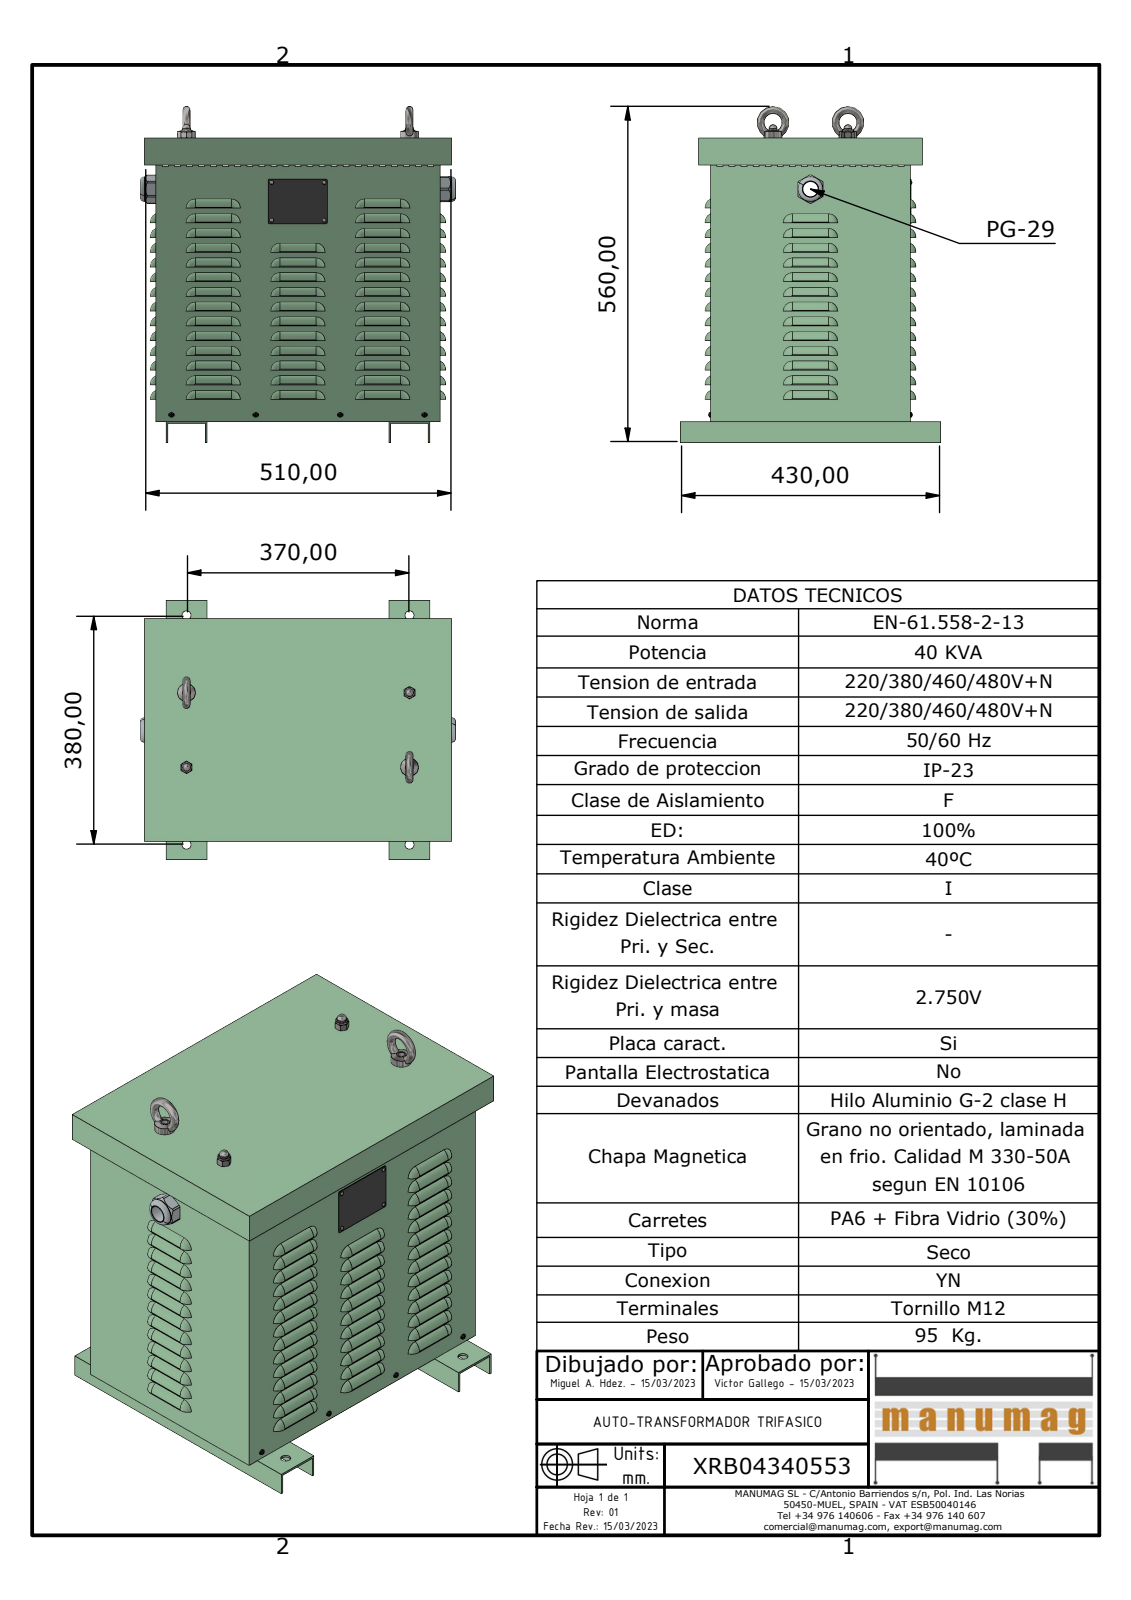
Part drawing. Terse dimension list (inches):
name: XRB04340553; JE040 - JE050 CUERPO; JE040 - JE050 BASE; JE040 - JE050 PATAS (+7 more)
written by: Autodesk Inventor 2023 (AUTOMOTIVE_DESIGN)
unit: in
bodies: 24 solids, 2403 faces (969 planar, 808 cylindrical, 626 other)
size: 22.047 × 20.606 × 16.969
volume: 190.1 in³; area: 4 290 in²
holes: 260× ⌀0.433, 4× ⌀0.157, 4× ⌀0.197, 4× ⌀0.398, 4× ⌀0.551, 4× ⌀0.591, 1× ⌀0.984, 1× ⌀1.496
bosses: 4× ⌀0.157, 4× ⌀0.143, 4× ⌀0.126, 2× ⌀1.181, 2× ⌀0.709, 2× ⌀0.535, 1× ⌀1.606, 1× ⌀1.469
rounds: 104× R0.551, 54× R0.276, 54× R0.591, 12× R0.127, 8× R0.098, 8× R0.295, 4× R0.079, 1× R0.939
face distances: 0.079, 18.504, 18.583, 12.953, 18.425, 12.874, 13.031, 0.118, 0.768, 13.72
hole spacings: 1.25, 2.819, 0.591, 1.102, 2.756, 1.756, 3.903, 5.543
